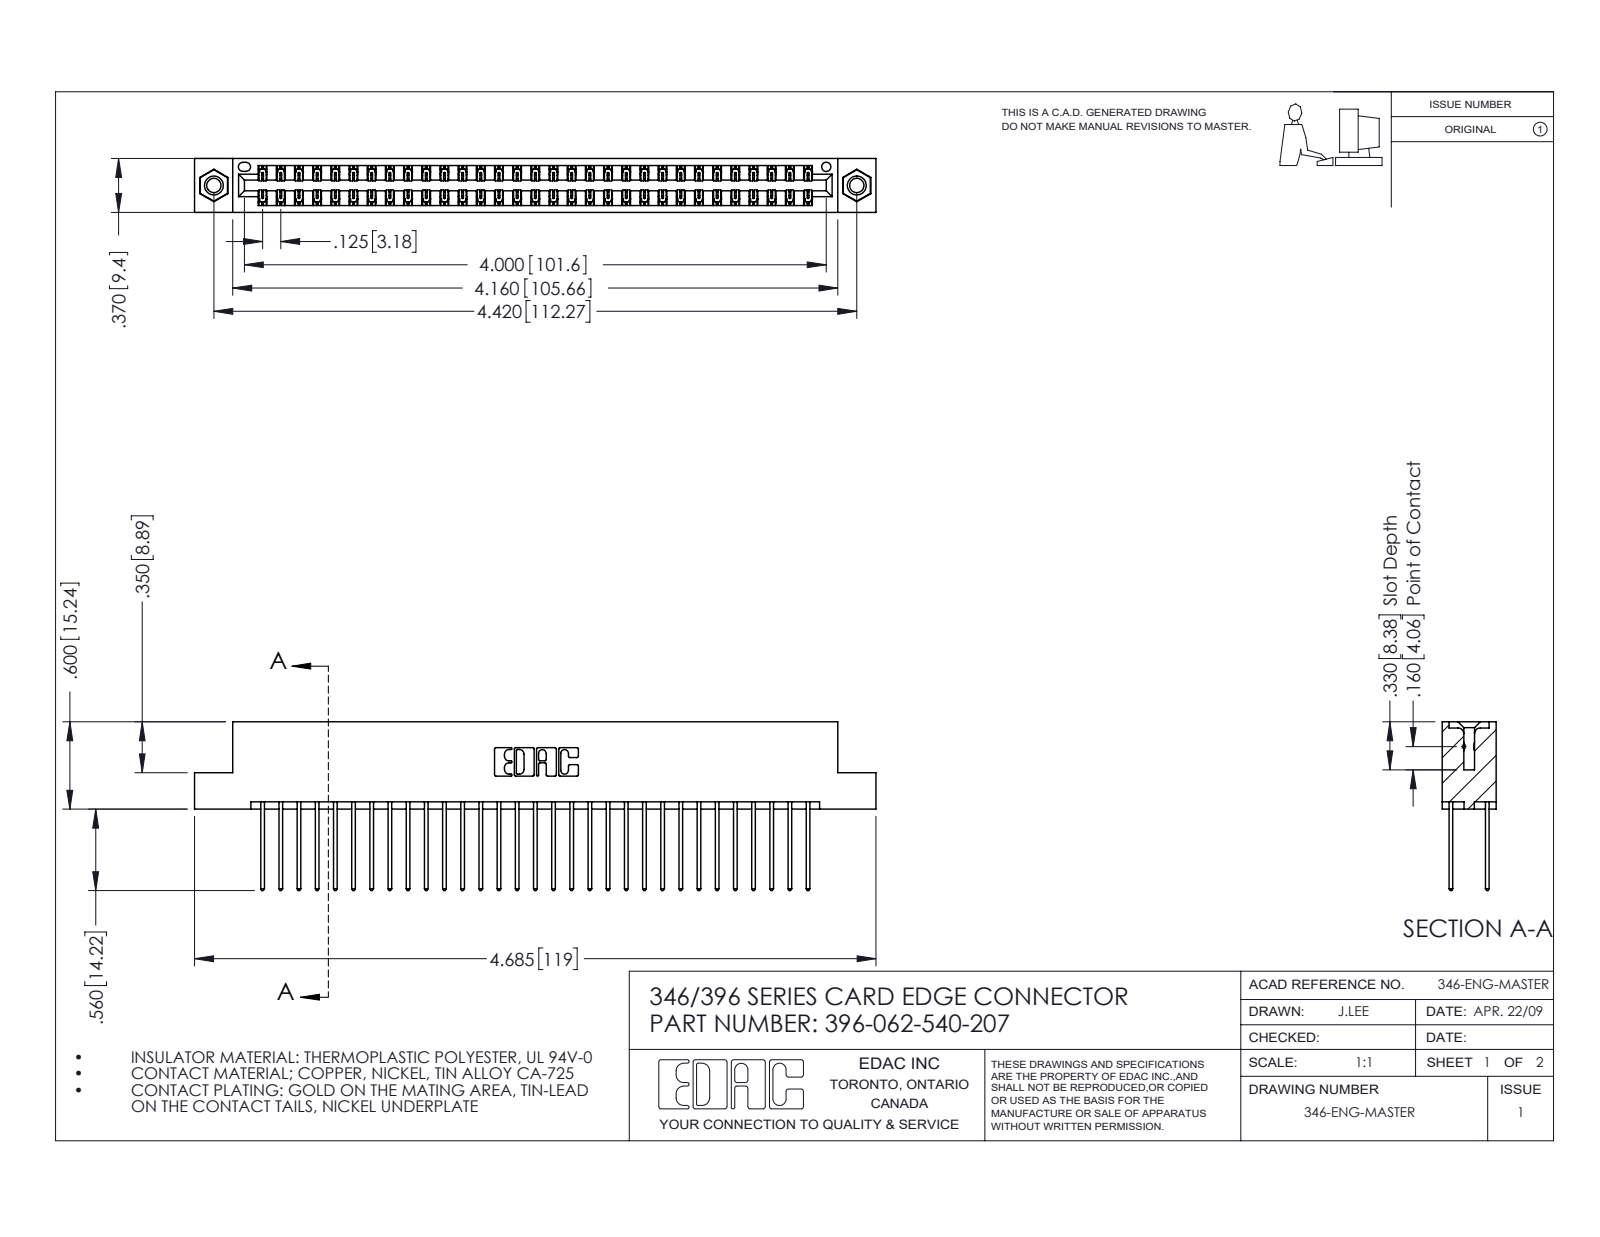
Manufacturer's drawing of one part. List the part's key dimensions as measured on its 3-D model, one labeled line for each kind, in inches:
Part name (STEP PRODUCT): 345-250-001_345-250-005-103; 396-062-540-207; 345-292-001_345-293-140; 346 Part_Flush Mounting Lugs - 0.156 Dia-TI
STEP written by: SolidWorks 2016 (CONFIG_CONTROL_DESIGN)
Units: inches
Bodies: 65 solids, 3406 faces (2278 planar, 1112 cylindrical, 16 other)
Overall size (bounding box): 4.685 × 1.16 × 0.37
Volume: 0.716 in³ · Surface area: 26.52 in²
Round holes (diameter × count): ⌀0.098 ×2, ⌀0.125 ×2, ⌀0.156 ×2, ⌀0.064 ×1
Round bosses / shafts (diameter × count): ⌀0.155 ×2
Partial cylindrical surfaces — rounded edges, fillets, slot ends (radius × count): R0.006 ×93, R0.01 ×62, R0.01 ×22, R0.007 ×6, R0.031 ×6, R0.026 ×3, R0.014 ×2, R0.022 ×2
Main face-to-face distances: 0.048, 0.322, 0.25, 0.072, 0.298, 0.025, 0.37, 0.275, 0.148, 0.222
Hole centre spacings: 0.246, 4.212, 4.42
